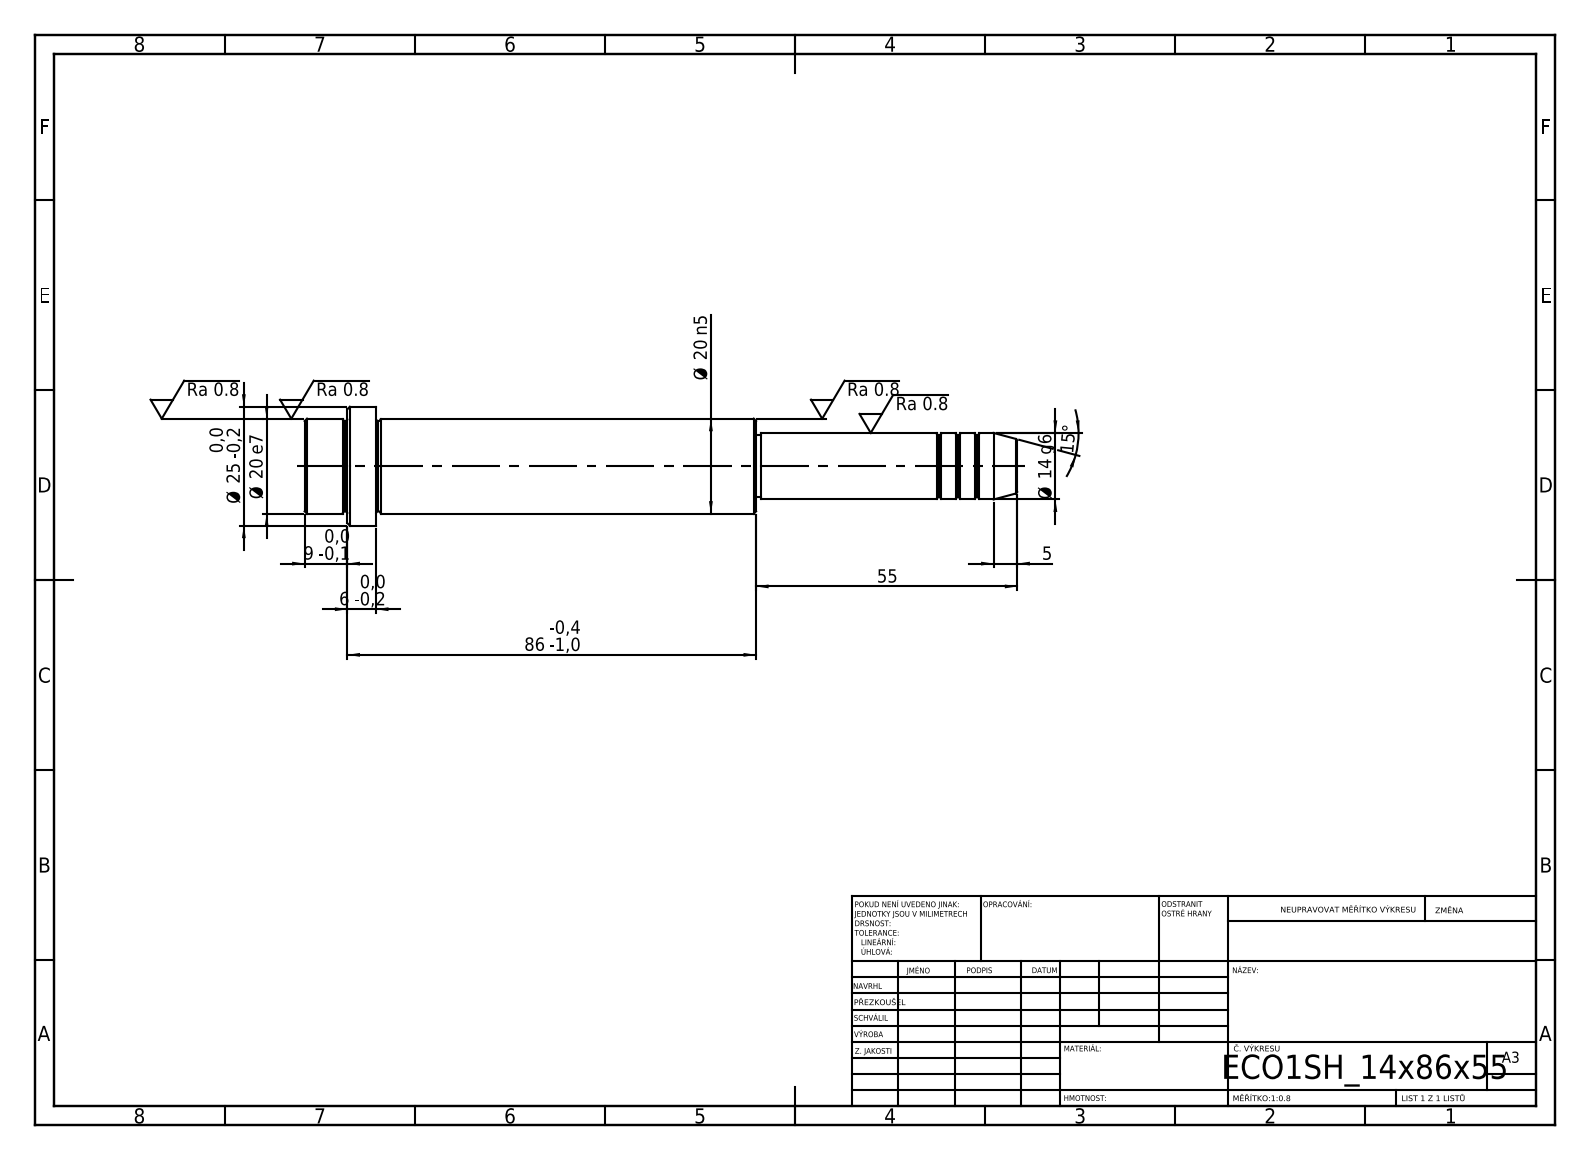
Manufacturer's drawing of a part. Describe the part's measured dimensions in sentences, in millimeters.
Its 3-D file was written by "SolidWorks 2019 (CONFIG_CONTROL_DESIGN)". It is 1 solid with 52 faces: 6 planar, 16 cylindrical and 30 other. Overall it measures 150 by 25 by 25 millimeters. Its volume is 39 088 cubic millimeters and its surface area 9 502 square millimeters. Round bosses or shafts: 1 of diameter 25, 1 of diameter 20, 1 of diameter 14, 1 of diameter 13. The main face-to-face distances are 15, 80, 95, 86, 6, 9, 55, 135, 141, 150.
